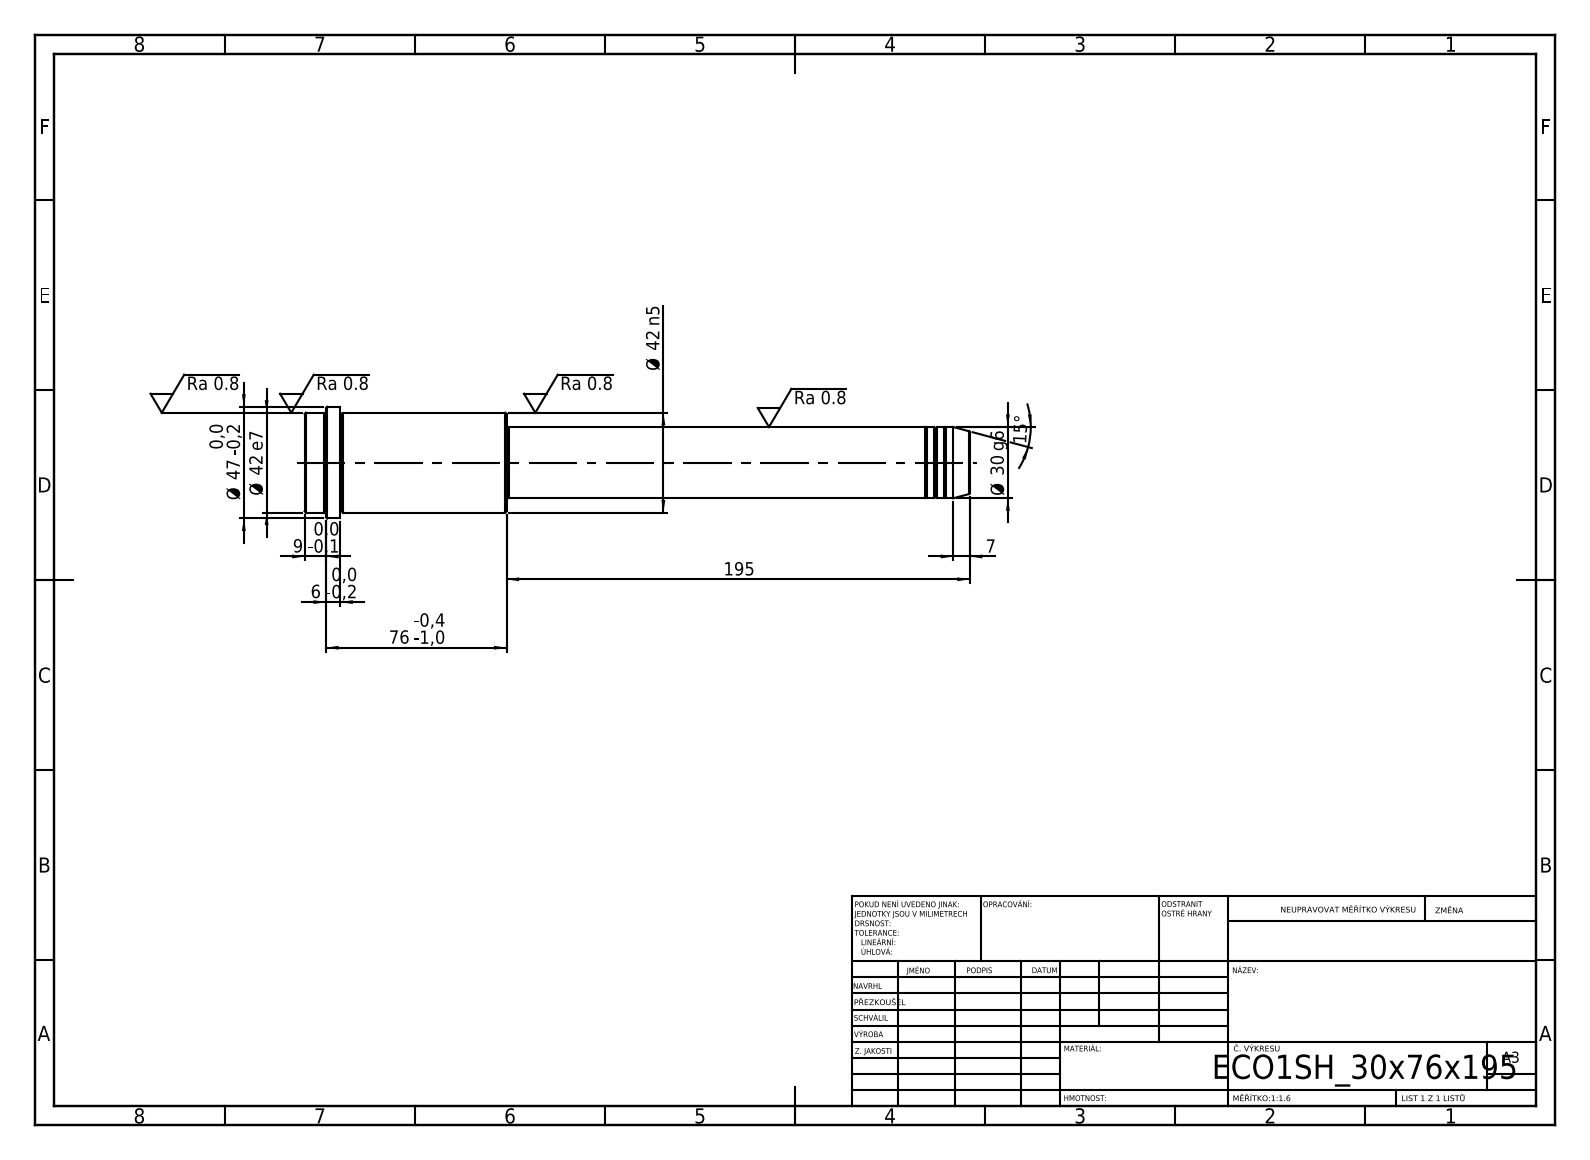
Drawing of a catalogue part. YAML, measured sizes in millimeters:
step_written_by: "SolidWorks 2019 (CONFIG_CONTROL_DESIGN)"
units: millimeters
bodies: {solids: 1, faces: 52, planar: 6, cylindrical: 16, other: 30}
overall_size: [280, 47, 47]
volume: 256792
surface_area: 33228
round_bosses_or_shafts:
  - {diameter: 47, count: 1}
  - {diameter: 42, count: 1}
  - {diameter: 30, count: 1}
  - {diameter: 29, count: 1}
face_to_face_distances: [85, 195, 280, 265, 70, 15, 271, 76, 6, 9]
